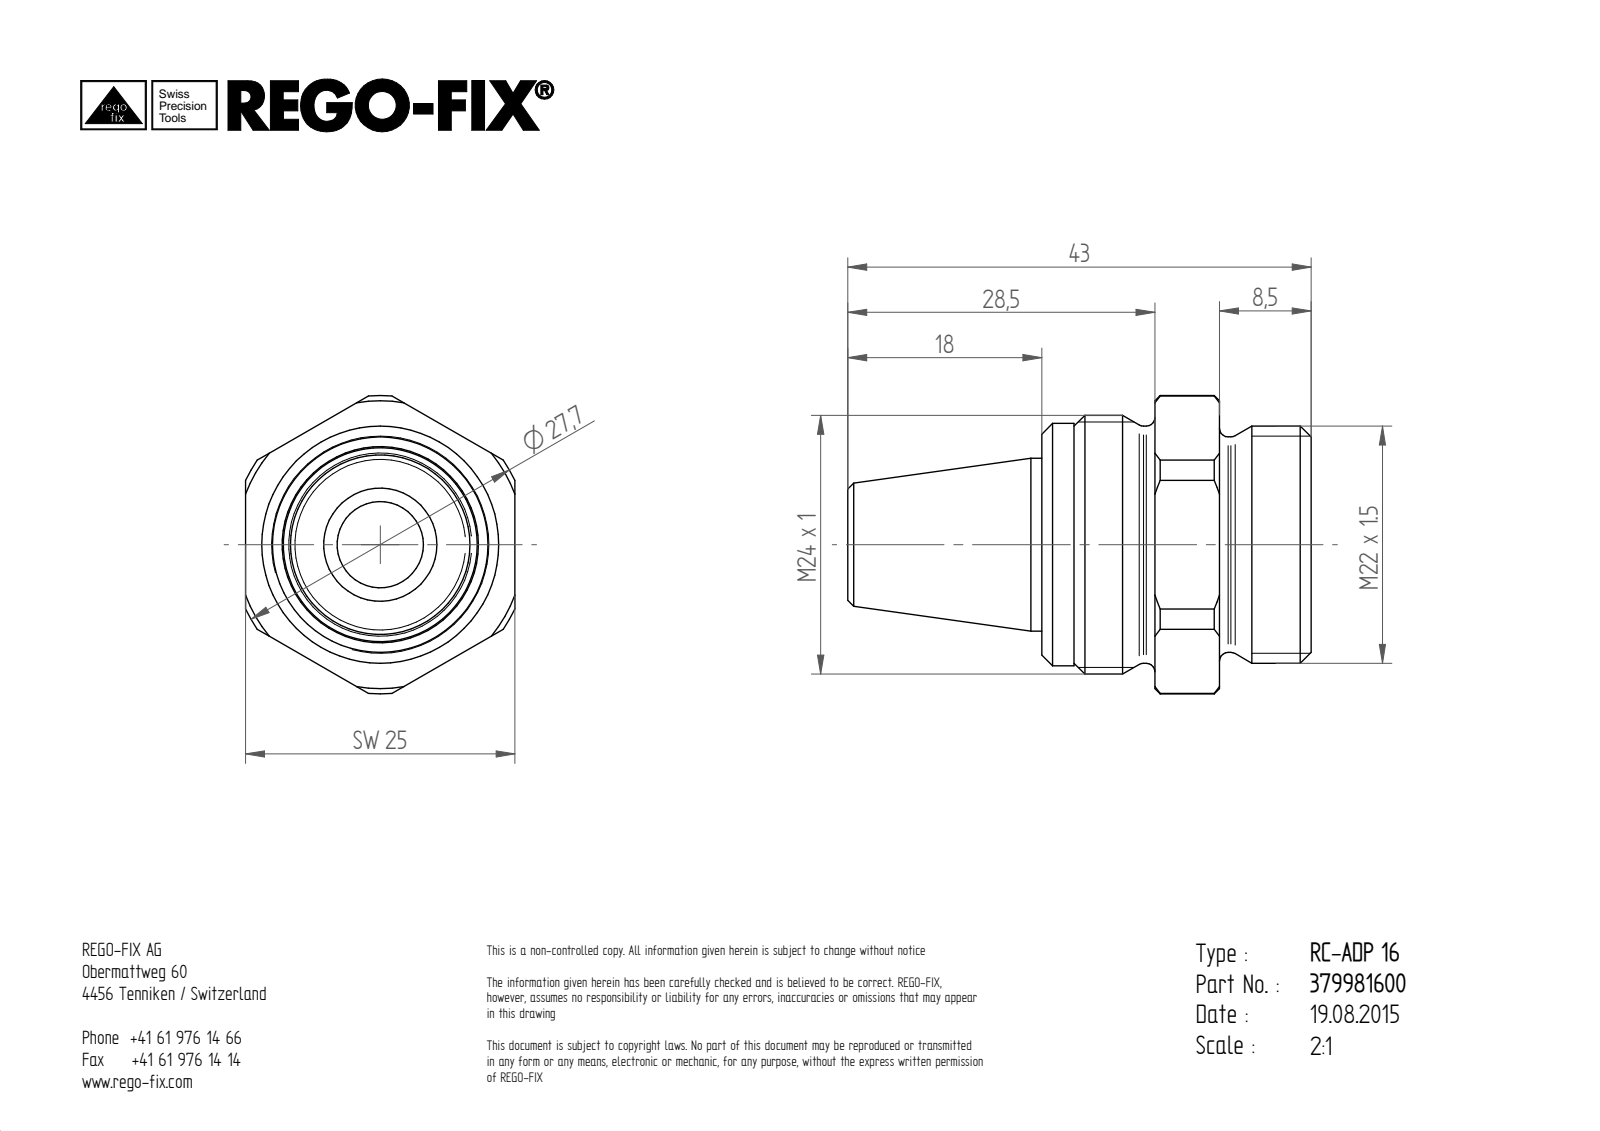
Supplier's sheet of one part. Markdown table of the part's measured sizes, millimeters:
| quantity | value |
| --- | --- |
| part name | 0012694; 0012701; 0012693 |
| STEP written by | Unknown (AUTOMOTIVE_DESIGN) |
| units | millimeters |
| bodies | 3 solids, 75 faces (18 planar, 19 cylindrical, 38 other) |
| overall size | 43 × 27.7 × 25 |
| volume | 9 132 mm³ |
| surface area | 8 023 mm² |
| round holes (diameter × count) | 8 × 1, 10.5 × 1, 18 × 1 |
| round bosses / shafts (diameter × count) | 24 × 1, 22.5 × 1, 22 × 1, 20 × 1, 16.8 × 1, 16.05 × 1 |
| partial cylindrical surfaces (radius × count) | 13.85 × 1 |
| main face-to-face distances | 25, 13.5, 3, 16.5, 10.5, 7.5, 6, 22, 14.5, 8.5 |
